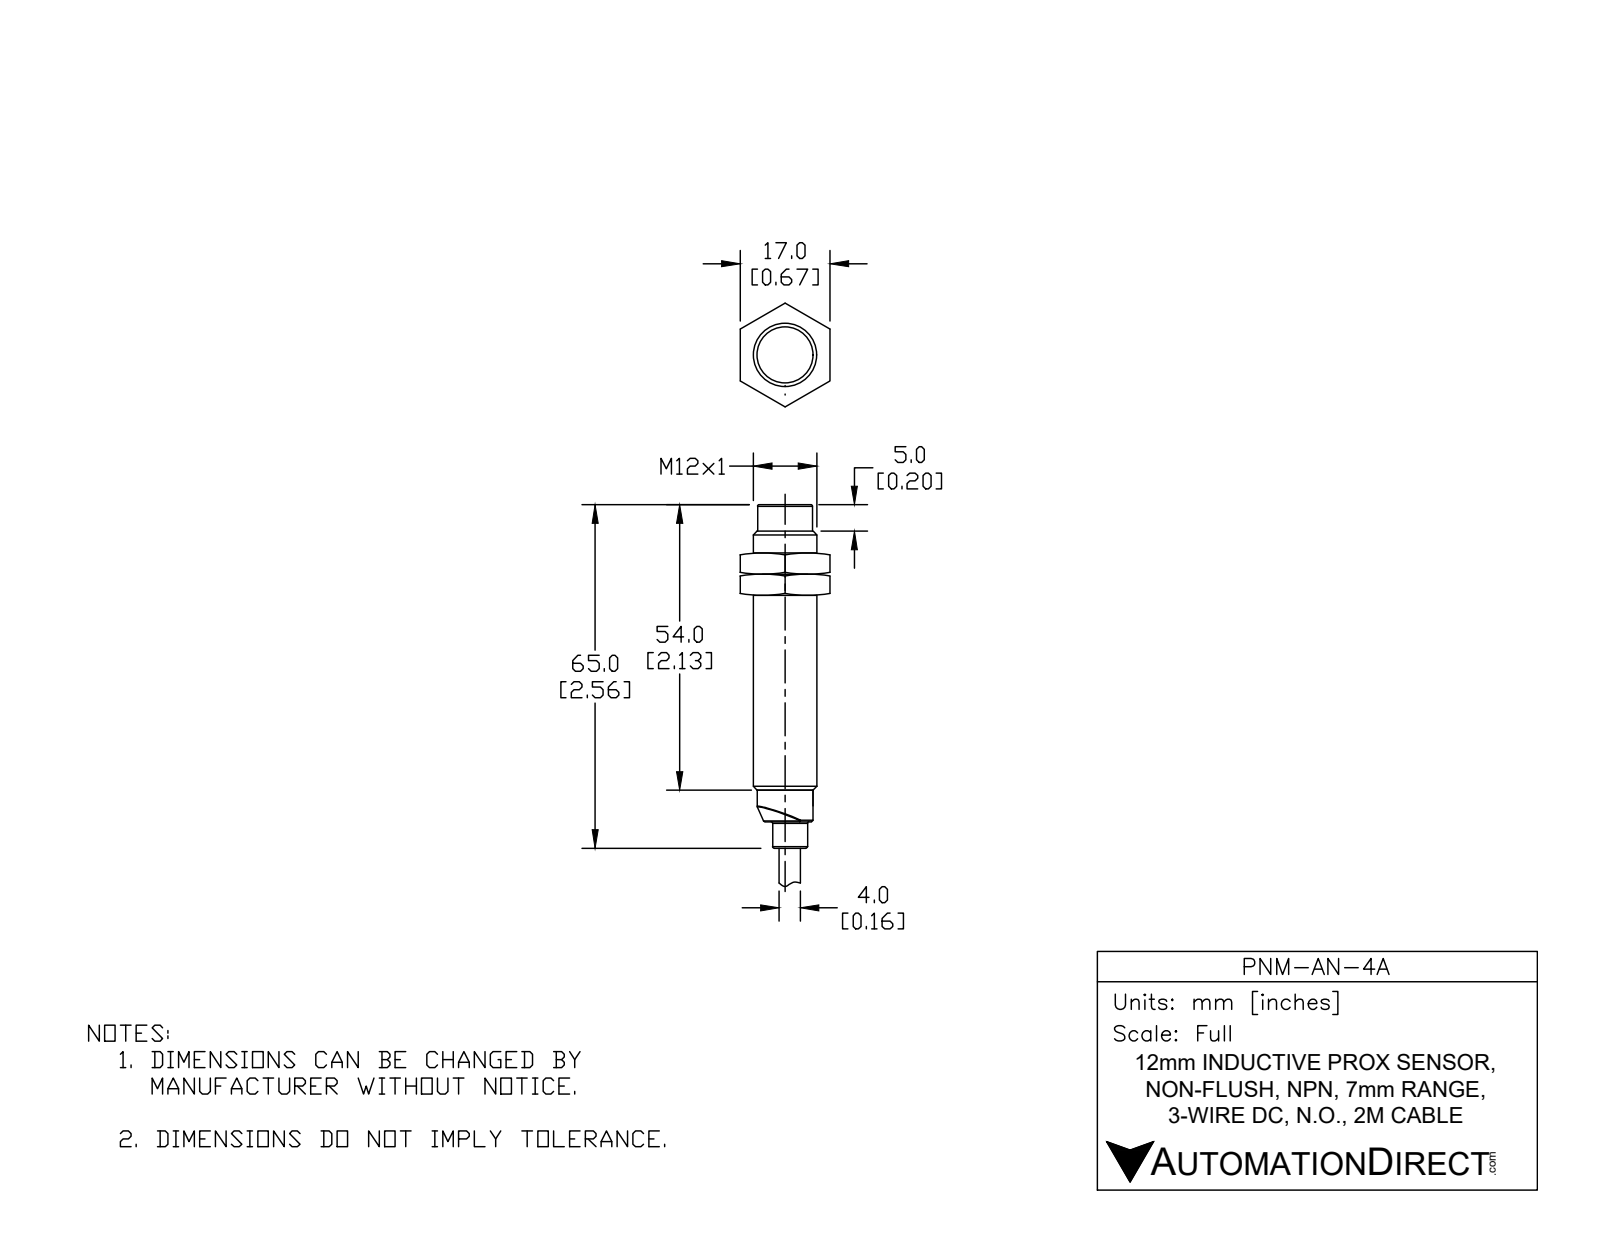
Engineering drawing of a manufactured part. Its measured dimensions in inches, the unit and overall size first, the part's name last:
Units: inches
Overall size (bounding box): 4.559 × 0.472 × 0.472
Round holes (diameter × count): ⌀0.161 ×1, ⌀0.401 ×1
Round bosses / shafts (diameter × count): ⌀0.472 ×1, ⌀0.417 ×1, ⌀0.415 ×1, ⌀0.384 ×1, ⌀0.26 ×1, ⌀0.157 ×1
Partial cylindrical surfaces — rounded edges, fillets, slot ends (radius × count): R0.091 ×1
Main face-to-face distances: 2.362, 2.559, 0.197, 4.559, 2.197, 2, 0.022, 2.34, 2.537, 4.537
Hole centre spacings: 0.039
Volume: 0.452 in³ · Surface area: 4.972 in²
Bodies: 1 solid, 68 faces (21 planar, 19 cylindrical, 28 other)
Part name (STEP PRODUCT): PNM-AN-4A
STEP written by: SolidWorks 2017 (AUTOMOTIVE_DESIGN)
